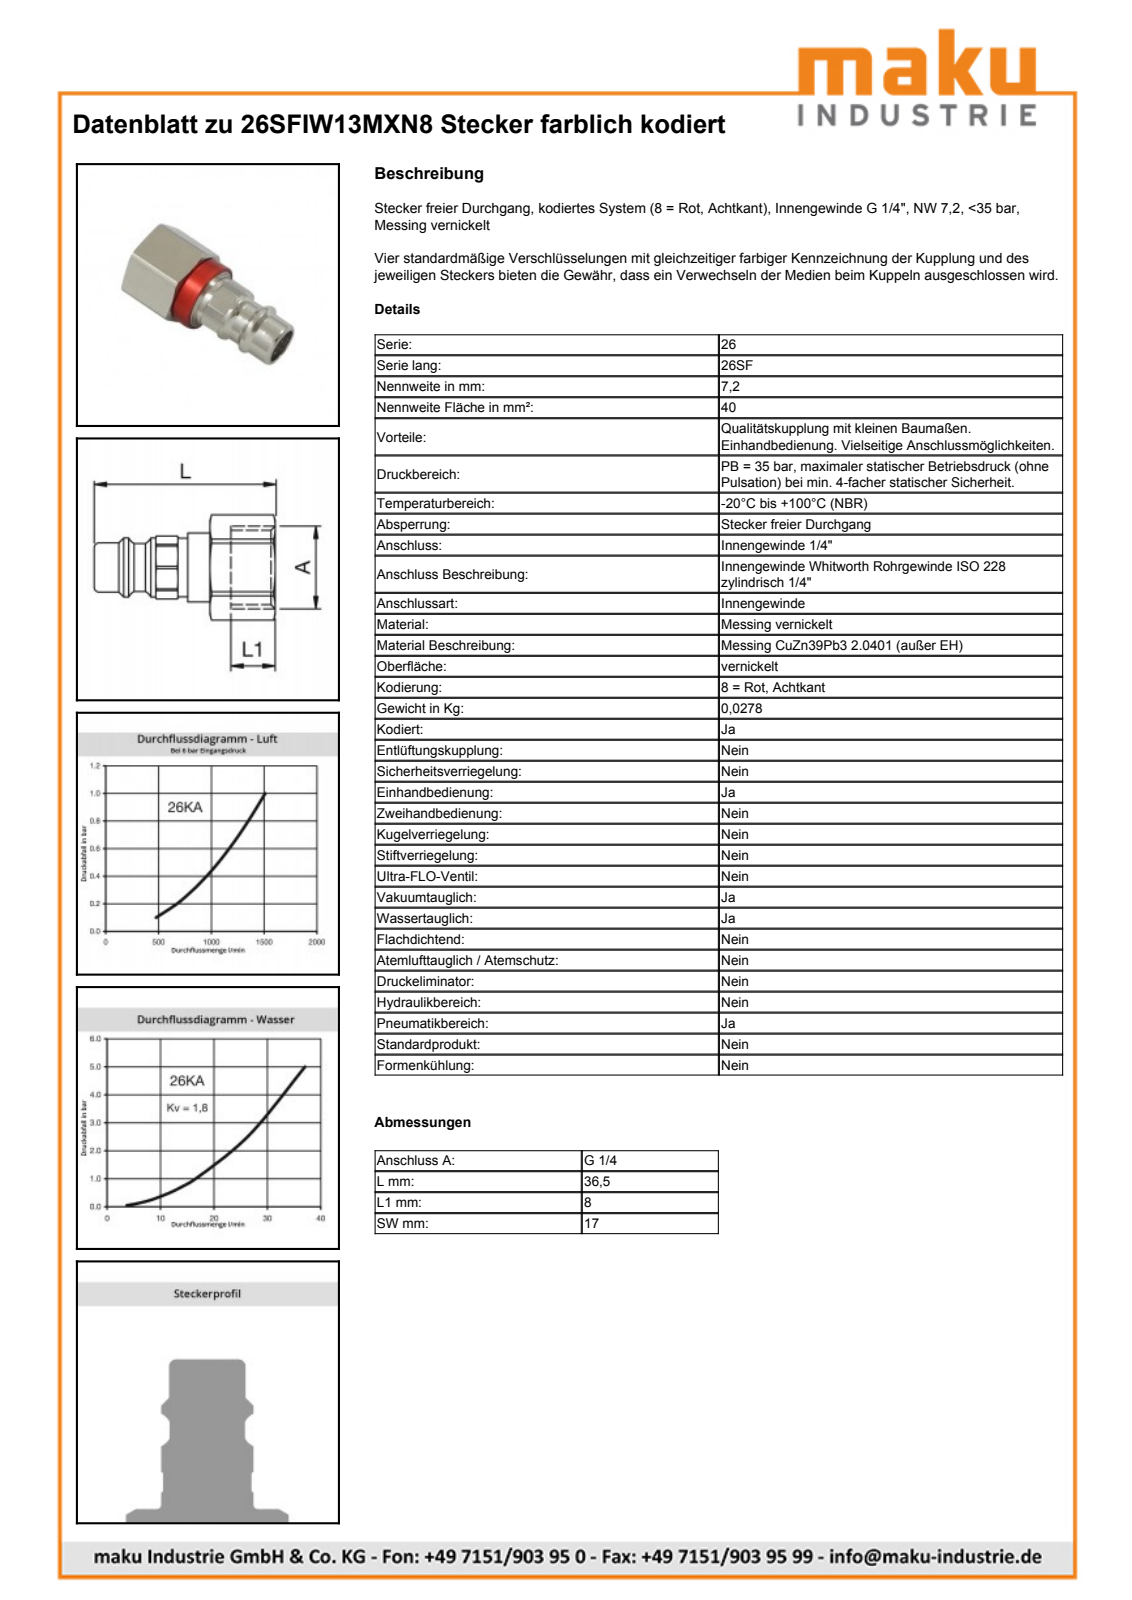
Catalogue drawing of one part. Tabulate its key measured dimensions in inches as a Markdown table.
| quantity | value |
| --- | --- |
| part name | D112681; D112676; D103012 |
| STEP written by | Autodesk Inventor 2013 (AUTOMOTIVE_DESIGN) |
| units | inches |
| bodies | 2 solids, 84 faces (21 planar, 25 cylindrical, 38 other) |
| overall size | 1.437 × 0.754 × 0.669 |
| volume | 0.219 in³ |
| surface area | 5.365 in² |
| round holes (diameter × count) | 0.309 × 1, 0.451 × 1, 0.545 × 1, 0.553 × 1 |
| round bosses / shafts (diameter × count) | 0.61 × 1, 0.551 × 1, 0.472 × 1, 0.469 × 1, 0.394 × 1, 0.384 × 1 |
| partial cylindrical surfaces (radius × count) | 0.252 × 1, 0.377 × 1 |
| main face-to-face distances | 0.669, 0.472, 0.512, 0.177, 0.689, 0.295, 0.118, 0.394, 0.098, 0.571 |
